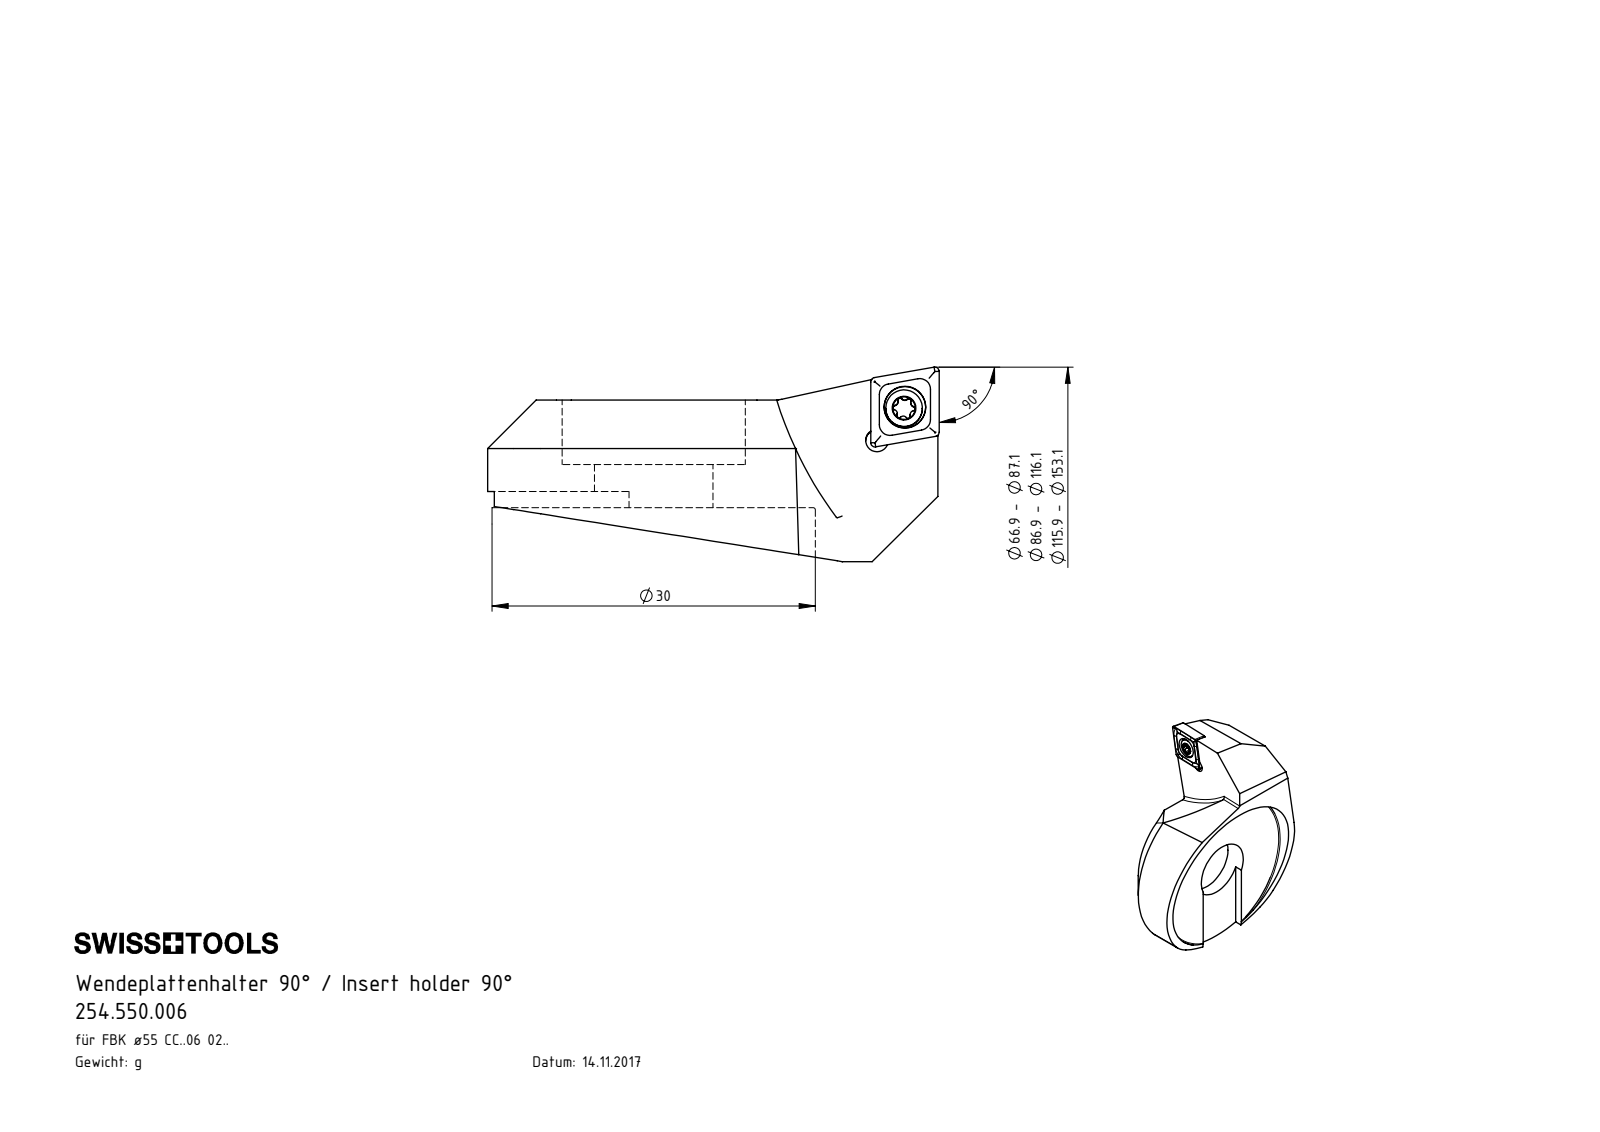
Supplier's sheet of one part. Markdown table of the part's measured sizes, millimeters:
| quantity | value |
| --- | --- |
| part name | F55.WCA.001.013; F55-WCA.001.013_D_fertigbearbeitet; WCA-ER2.001.005_A; CCMT060204 |
| STEP written by | SolidWorks 2017 (AUTOMOTIVE_DESIGN) |
| units | millimeters |
| bodies | 3 solids, 141 faces (39 planar, 45 cylindrical, 57 other) |
| overall size | 41.9 × 33.1 × 18.05 |
| volume | 7 725 mm³ |
| surface area | 3 934 mm² |
| round holes (diameter × count) | 2.05 × 1, 2.1 × 1, 2.8 × 1, 3.85 × 1, 11 × 1, 17 × 1, 30 × 1 |
| round bosses / shafts (diameter × count) | 3.4 × 1, 2.5 × 1 |
| partial cylindrical surfaces (radius × count) | 0.21 × 6, 0.36 × 5, 0.5 × 2, 10 × 2, 0.36 × 1, 5 × 1, 16.55 × 1, 20.9 × 1 |
| main face-to-face distances | 10, 6, 4, 8.5, 2.5, 1.5, 2.18, 5, 15, 9 |
| hole center spacings | 3.91, 4.04 |
